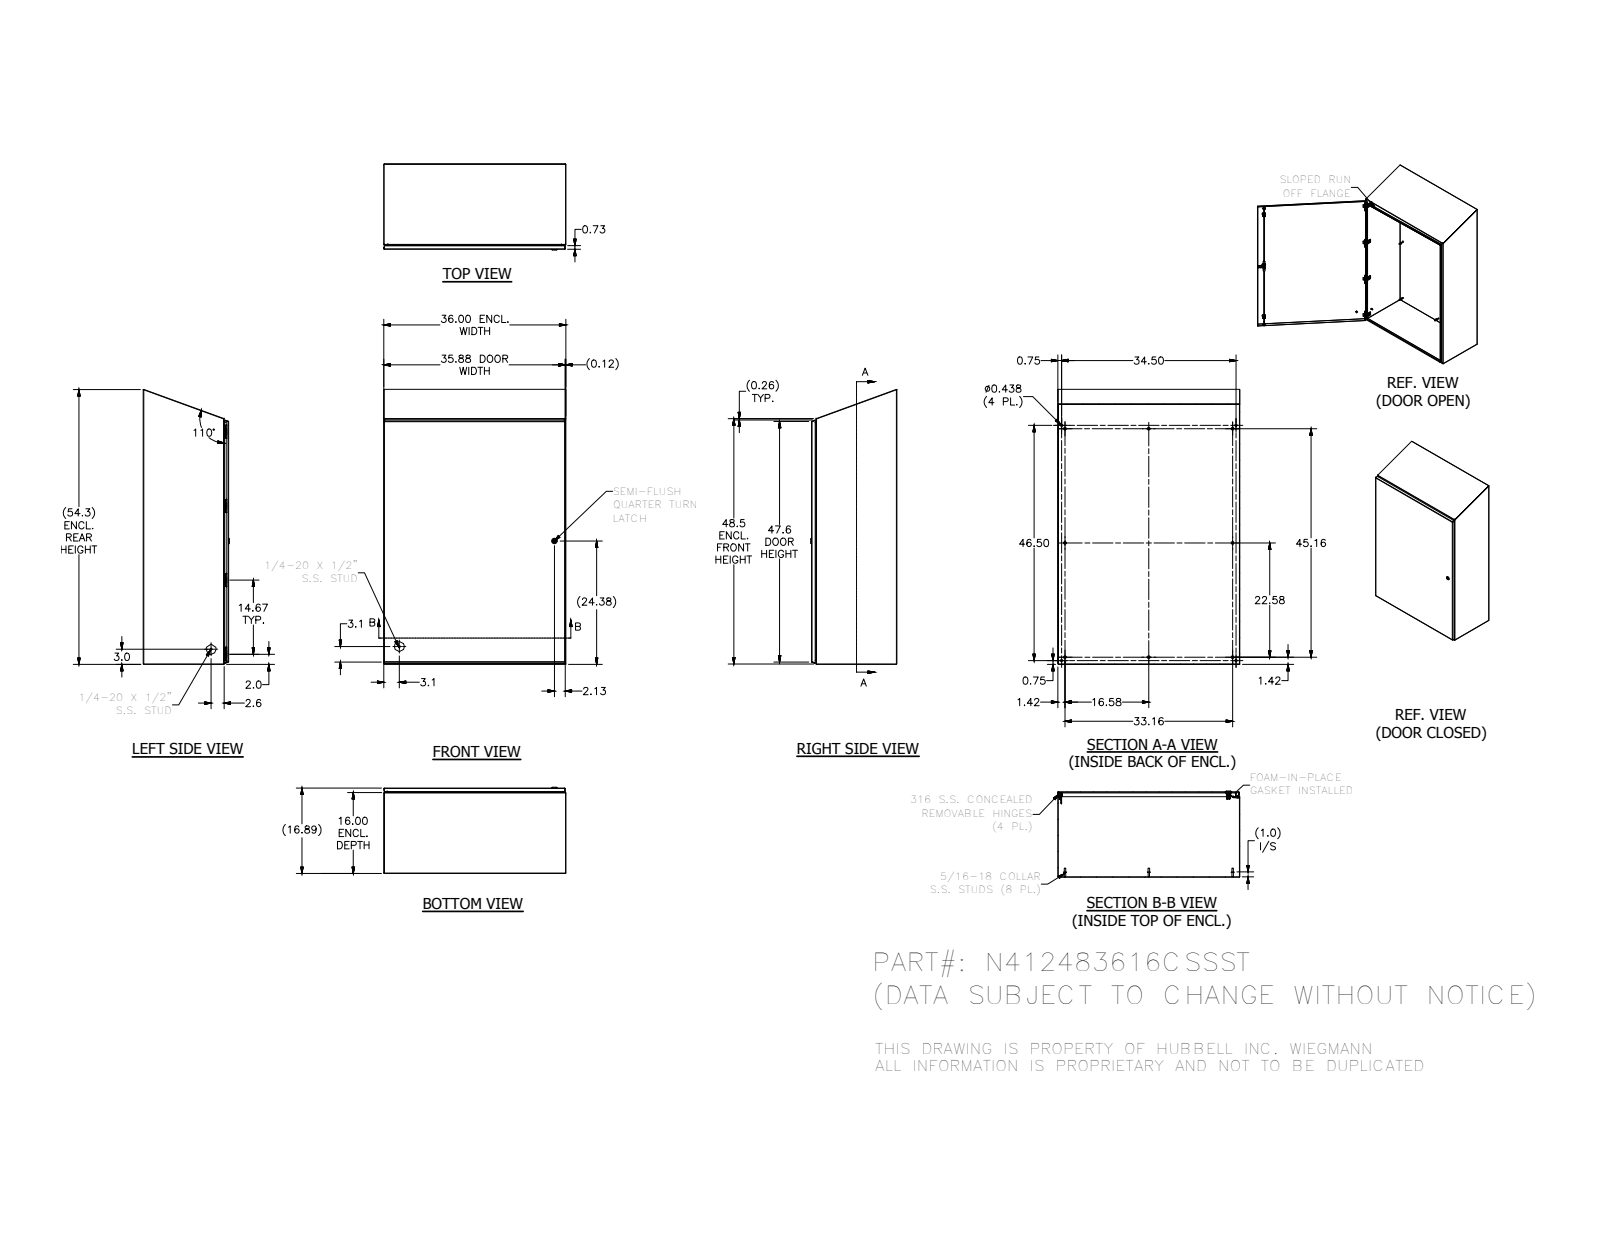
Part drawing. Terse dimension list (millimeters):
name: N412_CSSST-assm3pcblr; N412483616CSSSTBLR; HFW3161; HFW328176 (+8 more)
written by: Autodesk Inventor 2012 (AUTOMOTIVE_DESIGN)
unit: mm
bodies: 82 solids, 2675 faces (981 planar, 996 cylindrical, 698 other)
size: 1381.2 × 914.4 × 432.9
volume: 8 416 000 mm³; area: 8 945 000 mm²
holes: 8× ⌀2.4, 8× ⌀3.9, 8× ⌀4.2, 8× ⌀4.4, 8× ⌀4.7, 5× ⌀4, 5× ⌀5, 4× ⌀4.2, 4× ⌀11.1, 2× ⌀2.7, 2× ⌀4.1, 2× ⌀4.3
bosses: 18× ⌀6.4, 8× ⌀14.3, 8× ⌀9.1, 8× ⌀8.1, 8× ⌀7.6, 8× ⌀7, 8× ⌀6.5, 8× ⌀4.2
rounds: 50× R1.3, 34× R0.4, 33× R0.8, 32× R3.2, 30× R0.3, 20× R0.5, 16× R0.8, 16× R3
face distances: 1.9, 427.1, 425.2, 428.9, 912.5, 910.6, 914.4, 404.5, 22.5, 20.7
hole spacings: 372.5, 745.1, 372.5, 1117.6, 12.7, 16.7, 33.2, 372.7
